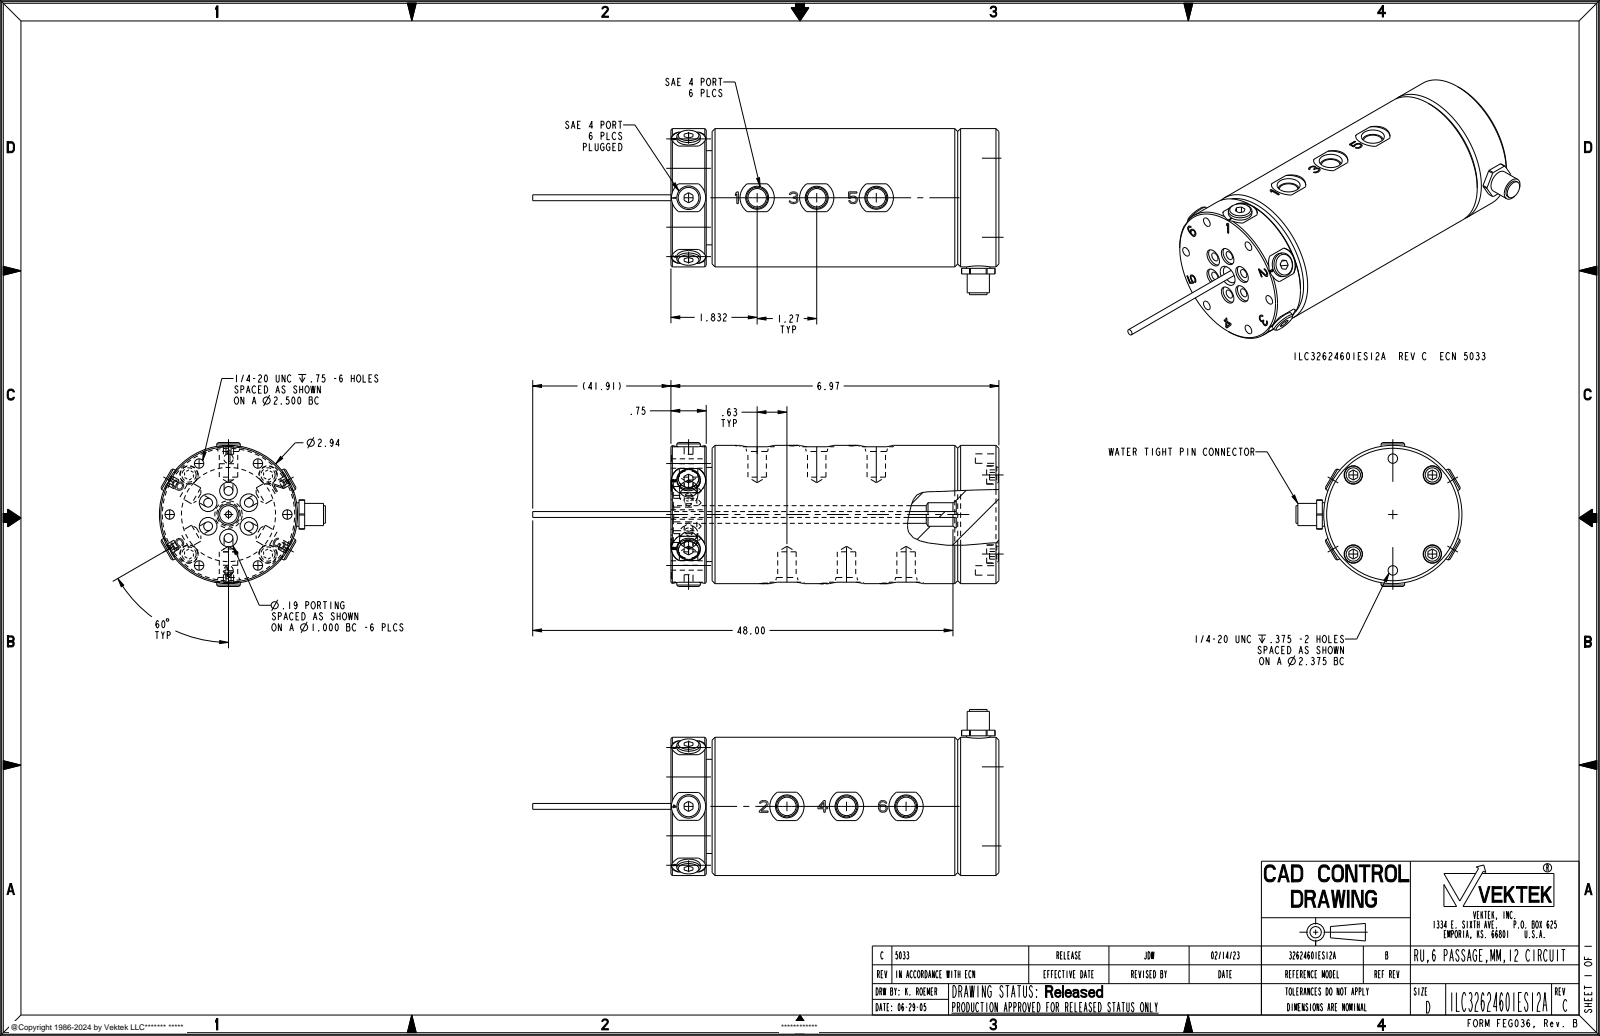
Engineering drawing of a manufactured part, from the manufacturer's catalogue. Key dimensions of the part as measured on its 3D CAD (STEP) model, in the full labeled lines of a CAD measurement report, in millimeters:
Part name (STEP PRODUCT): ILC32624601ES12A
STEP written by: CREO PARAMETRIC BY PTC INC, 2021164 (AUTOMOTIVE_DESIGN)
Units: millimetres
Bodies: 1 solid, 1018 faces (772 planar, 160 cylindrical, 86 other)
Overall size (bounding box): 251.6 × 89.6 × 77.6
Volume: 737 900 mm³ · Surface area: 74 450 mm²
Round holes (diameter × count): ⌀4.7 ×9, ⌀10 ×9, ⌀9.5 ×7, ⌀5.1 ×6, ⌀9.9 ×4, ⌀5.1 ×2, ⌀12.7 ×1
Round bosses / shafts (diameter × count): ⌀12.7 ×4, ⌀9.5 ×4, ⌀74.6 ×1, ⌀50.8 ×1, ⌀12 ×1, ⌀9.4 ×1, ⌀3.2 ×1
Partial cylindrical surfaces — rounded edges, fillets, slot ends (radius × count): R9.2 ×9, R9 ×1
Main face-to-face distances: 177, 158, 19.1, 3.2, 154.8, 22.2, 2.3, 75.4, 11.4, 66.2
Hole centre spacings: 12.7, 34.2, 43.2, 31.8, 21.7, 21.7, 22, 31.8
